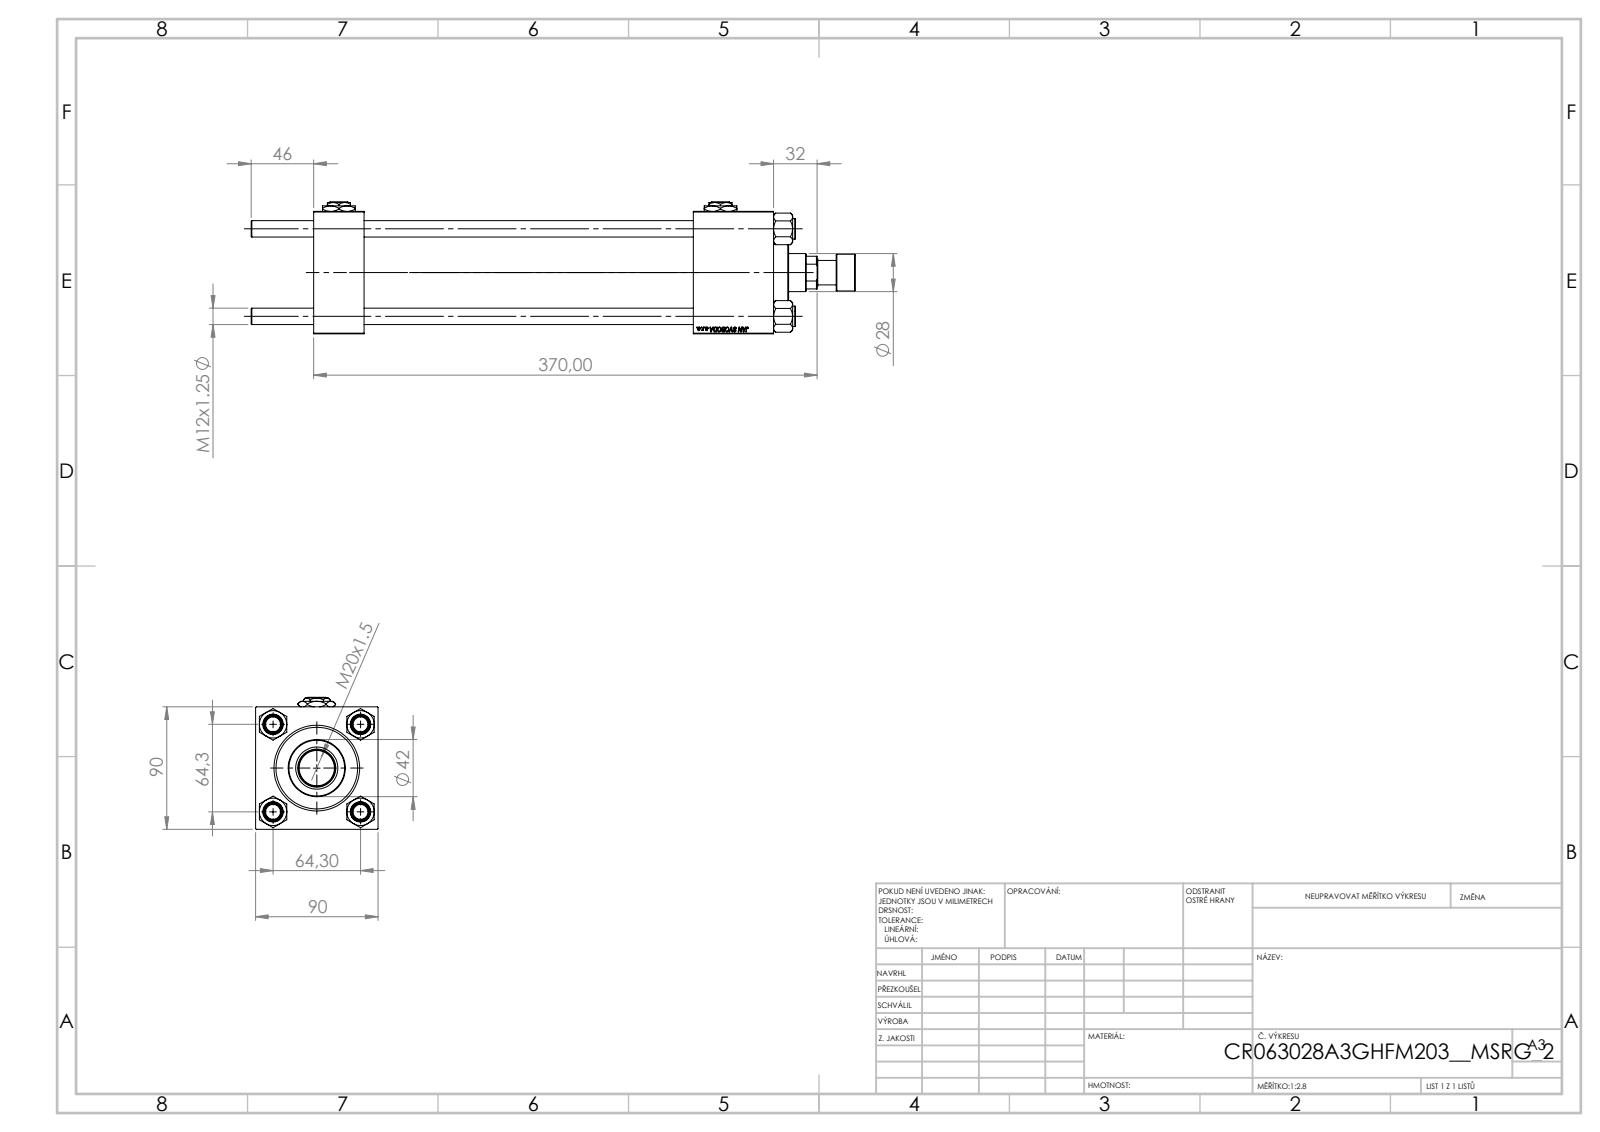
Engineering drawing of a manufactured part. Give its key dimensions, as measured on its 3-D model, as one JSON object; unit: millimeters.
{"part_name": "V215CR_ROD_END_F; CR025_012_A_0_G_A_G_M_020_+#_##_TYCINKA; Zatka_pro_OIL_PORT; NUT_M5 (+3 more)", "step_written_by": "SolidWorks 2019 (CONFIG_CONTROL_DESIGN)", "units": "millimeters", "bodies": {"solids": 14, "faces": 1247, "planar": 571, "cylindrical": 92, "other": 584}, "overall_size": [444, 97, 90], "volume_mm3": 1296000, "surface_area_mm2": 322889, "round_holes": [[12, 4], [7, 2], [20.96, 2], [30, 2], [18.5, 1], [28, 1], [31, 1], [50, 1], [60, 1], [63, 1]], "round_bosses_or_shafts": [[15, 4], [69, 1], [42, 1], [27, 1], [18, 1]], "face_to_face_distances": [90, 37, 338, 301, 59, 279, 242, 309.3, 272.3, 30.3], "hole_center_spacings": [45.47, 64.3, 90.93, 280.5]}
